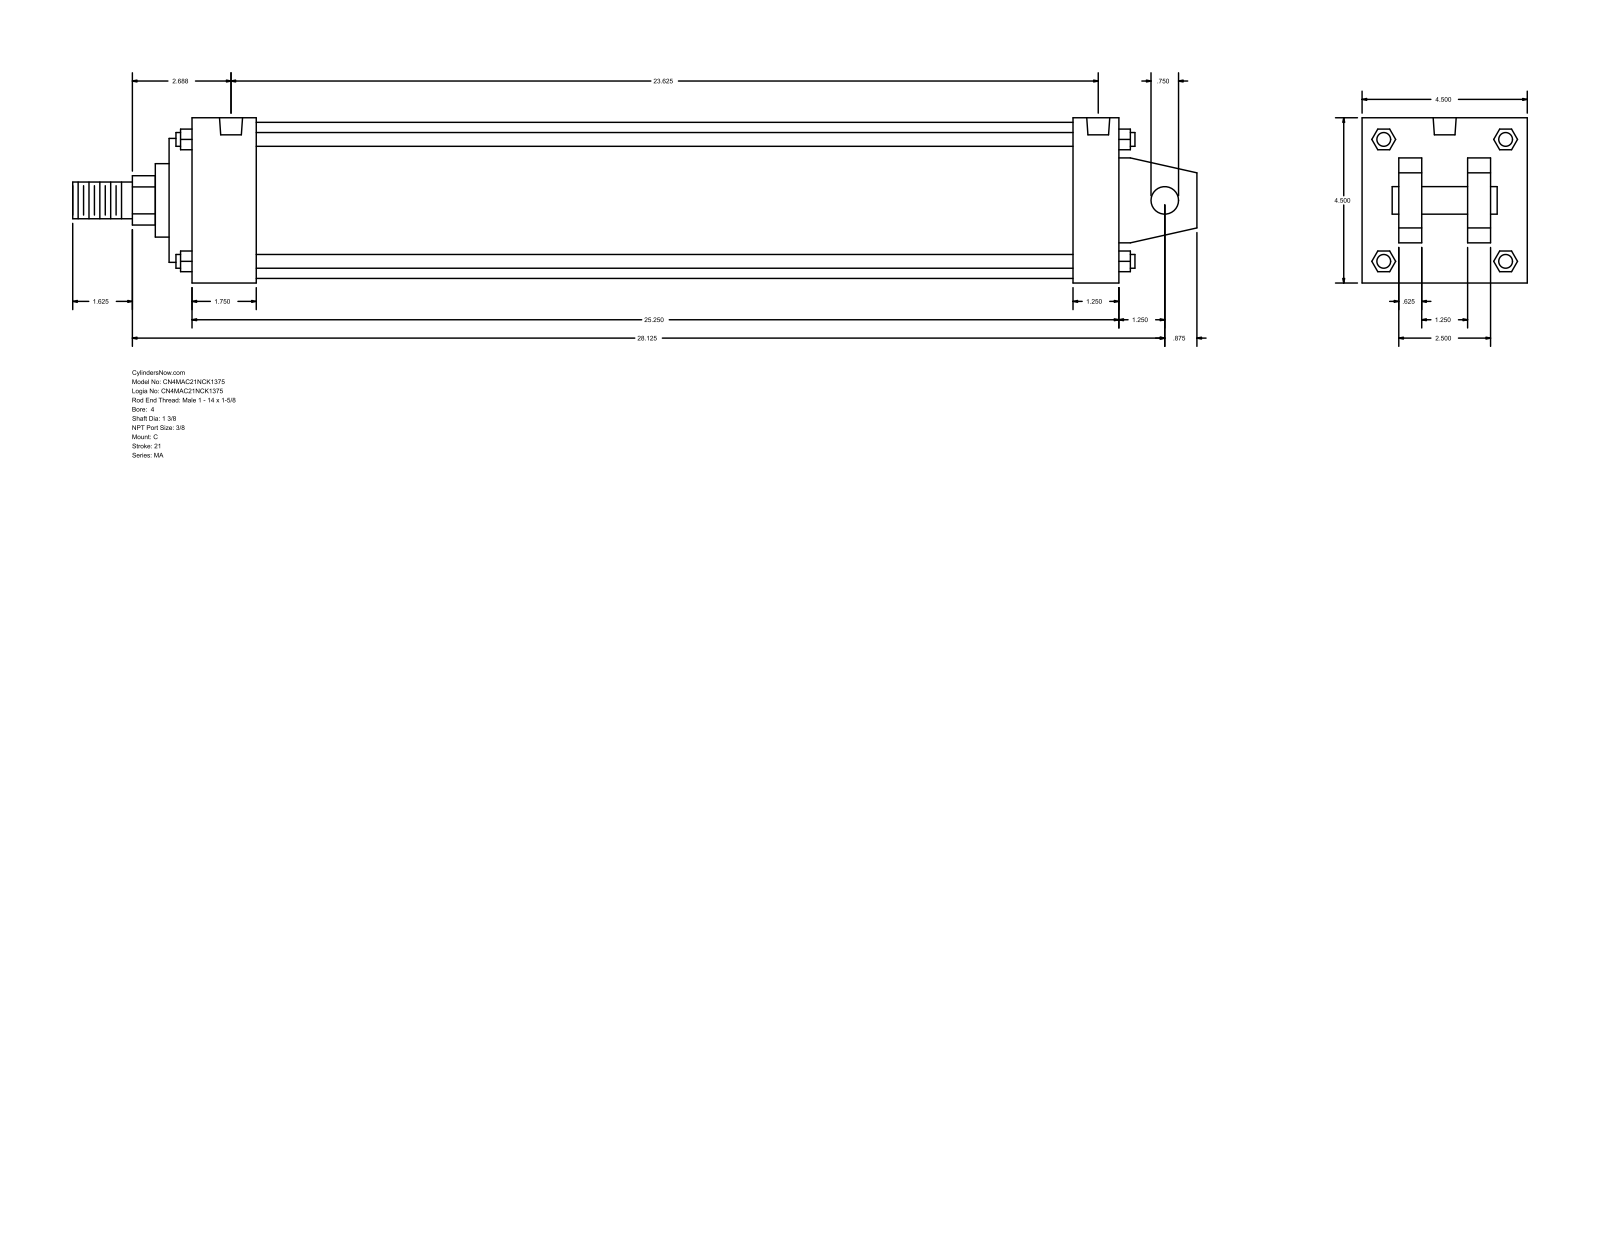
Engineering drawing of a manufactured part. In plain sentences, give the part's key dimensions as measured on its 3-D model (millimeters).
The part is named "MA_C__0400_1.375". Its 3-D file was written by "GSSL Pune (CONFIG_CONTROL_DESIGN)". It is 0 solids with 141 faces: 109 planar, 32 cylindrical and 0 other. Overall it measures 777.88 by 114.3 by 114.3 millimeters. Round holes: 4 of diameter 11.11, 2 of diameter 15.93. Round bosses or shafts: 4 of diameter 9.53, 1 of diameter 107.95, 1 of diameter 85.72, 1 of diameter 50.8, 1 of diameter 34.92, 1 of diameter 25.4, 1 of diameter 19.05. Partial cylindrical surfaces (rounded edges, fillets, slot ends): 1 of radius 17.06. The main face-to-face distances are 114.3, 15.87, 641.35, 73.03, 41.27, 25.4, 88.9, 47.63, 657.22, 625.48. The hole center spacings are 590.55, 4.76, 4.77, 595.31, 595.32, 600.08.
